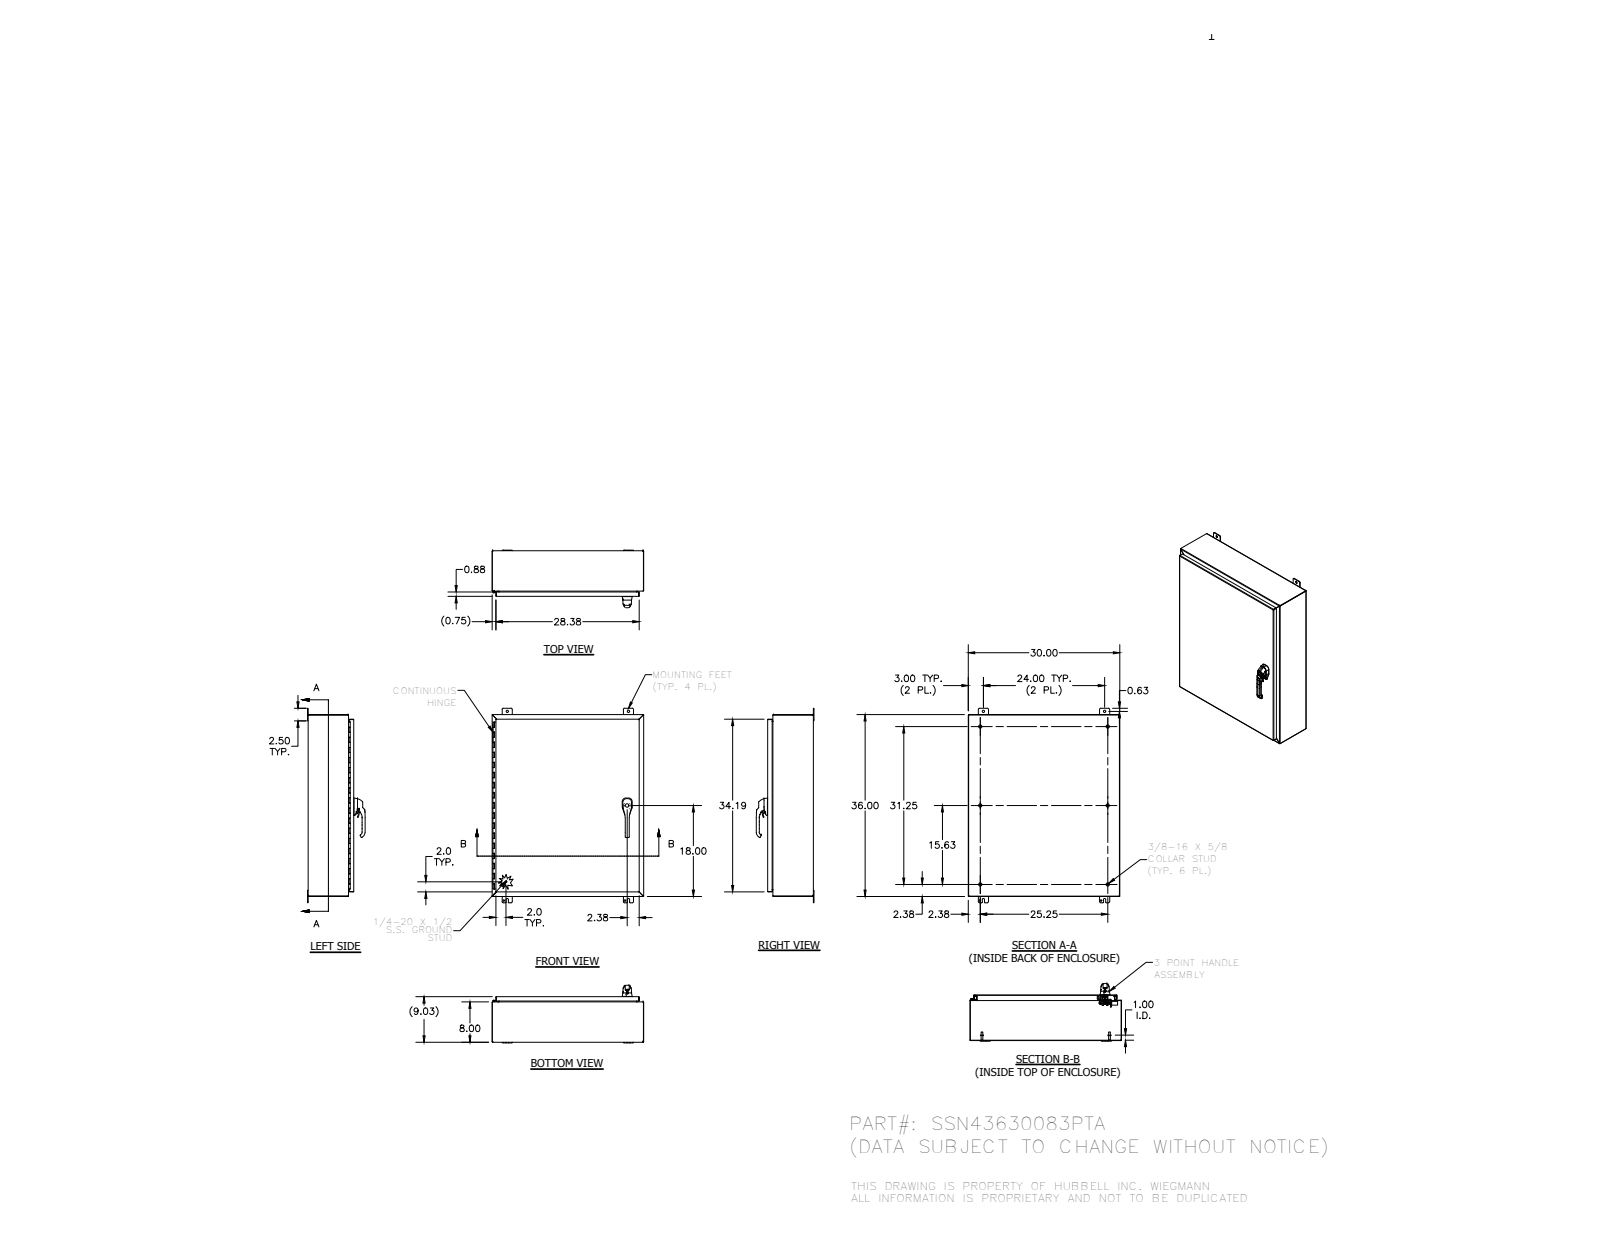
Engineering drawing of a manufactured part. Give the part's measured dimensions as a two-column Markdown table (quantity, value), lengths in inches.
| quantity | value |
| --- | --- |
| part name | SSN436303PTALID; 1091-903_AF0_1; 1091-76; 7379-M6-8X25_AF0 (+8 more) |
| STEP written by | SolidWorks 2014 (AUTOMOTIVE_DESIGN) |
| units | inches |
| bodies | 58 solids, 3229 faces (1088 planar, 1352 cylindrical, 789 other) |
| overall size | 38.5 × 30 × 11.408 |
| volume | 292.7 in³ |
| surface area | 7 627 in² |
| round holes (diameter × count) | 0.262 × 8, 0.187 × 4, 0.313 × 4, 0.438 × 4, 0.213 × 3, 0.281 × 3, 0.241 × 2, 0.25 × 2, 0.252 × 2, 0.315 × 2, 0.4 × 2, 0.402 × 2 |
| round bosses / shafts (diameter × count) | 0.625 × 6, 0.33 × 6, 0.236 × 3, 1 × 2, 0.563 × 2, 0.533 × 2, 0.531 × 2, 0.5 × 2 |
| partial cylindrical surfaces (radius × count) | 0.02 × 172, 0.012 × 113, 0.125 × 26, 0.031 × 24, 0.019 × 21, 0.105 × 20, 0.25 × 20, 0.025 × 16 |
| main face-to-face distances | 0.074, 8.959, 8.885, 9.033, 29.926, 35.926, 7.926, 1.033, 29.852, 30 |
| hole center spacings | 0.38, 0.492, 0.76, 24, 0.886, 1.593, 26.428, 36 |
